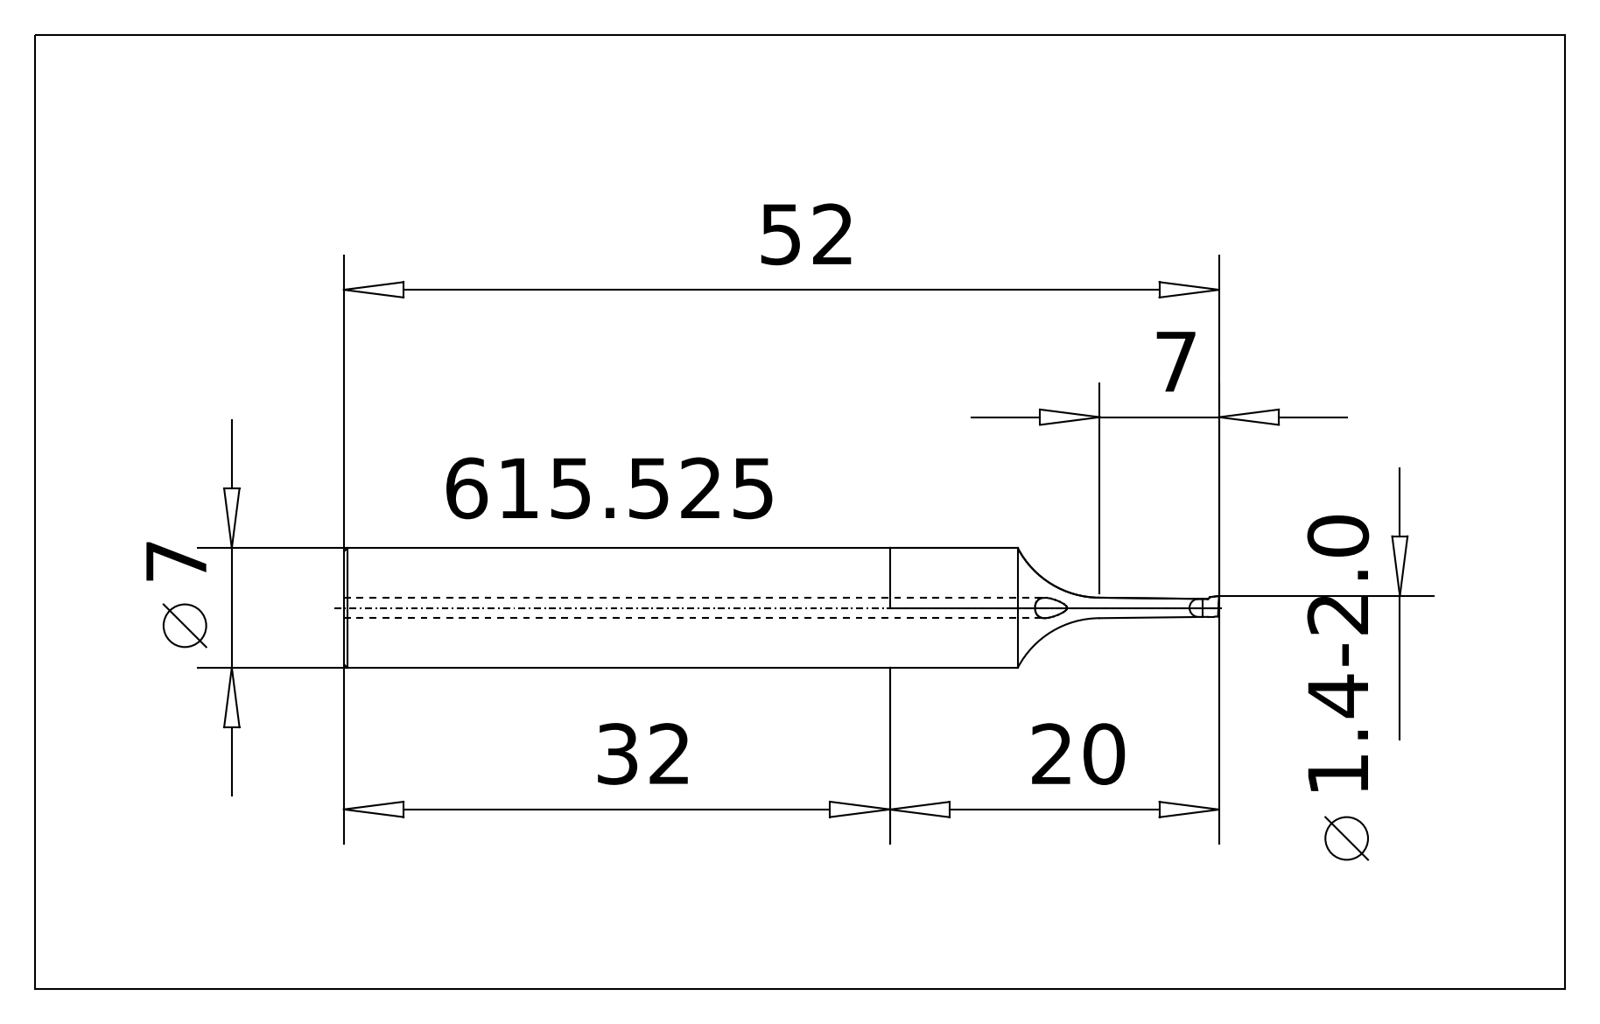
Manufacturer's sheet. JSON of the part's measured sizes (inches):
{"step_written_by": "ACIS (automotive_design)", "units": "inches", "bodies": {"solids": 1, "faces": 25, "planar": 8, "cylindrical": 5, "other": 12}, "overall_size": [2.02, 0.276, 0.276], "volume_in3": 0.092, "surface_area_in2": 1.758, "round_holes": [[0.047, 1]], "round_bosses_or_shafts": [[0.276, 1]], "partial_cylinders_radius": [[0.02, 1]], "face_to_face_distances": [1.457]}
